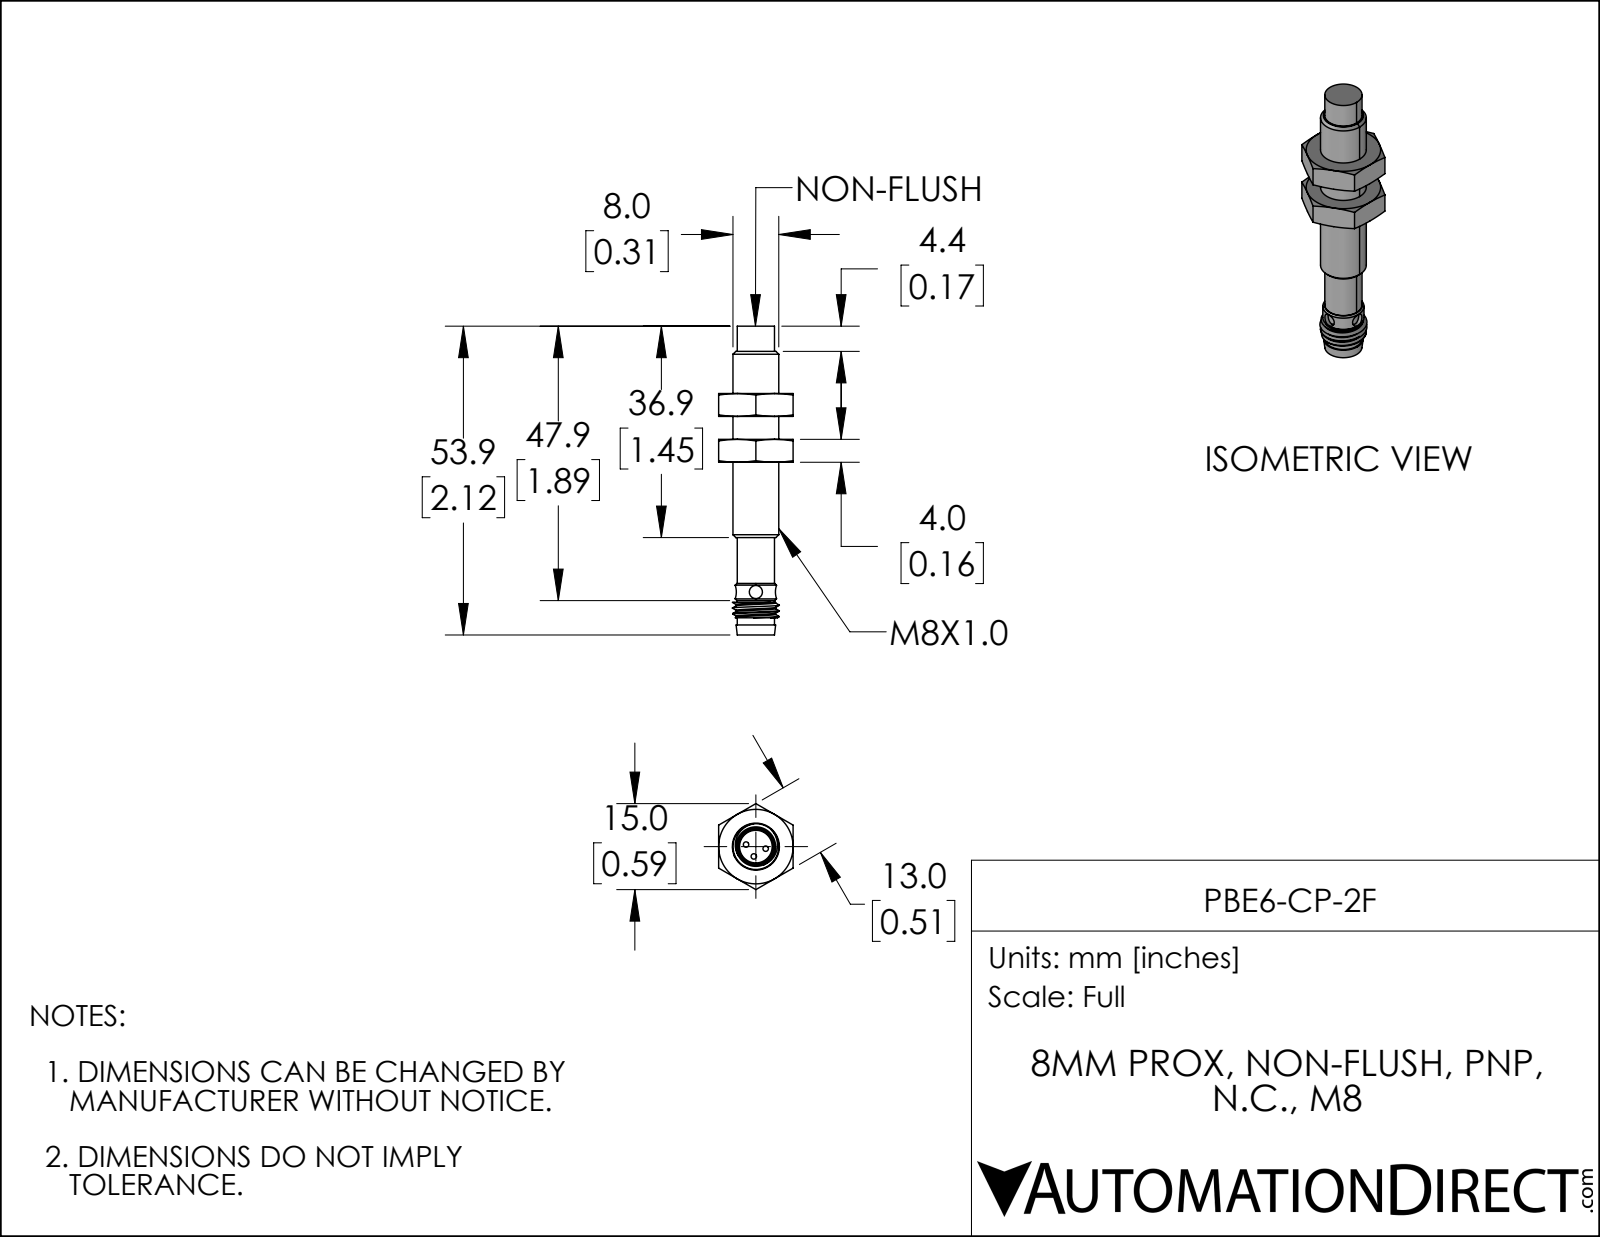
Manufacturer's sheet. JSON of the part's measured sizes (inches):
{"part_name": "DSD-0264", "step_written_by": "SolidWorks 2019 (AUTOMOTIVE_DESIGN)", "units": "inches", "bodies": {"solids": 1, "faces": 43, "planar": 12, "cylindrical": 19, "other": 12}, "overall_size": [2.122, 0.324, 0.324], "volume_in3": 0.138, "surface_area_in2": 2.44, "round_holes": [[0.091, 2], [0.224, 1]], "round_bosses_or_shafts": [[0.037, 3], [0.315, 1], [0.283, 1], [0.256, 1]], "partial_cylinders_radius": [[0.113, 1]], "face_to_face_distances": [1.925, 2.004, 0.079, 1.898, 0.028, 0.106, 0.118, 1.453, 0.445, 0.472]}
